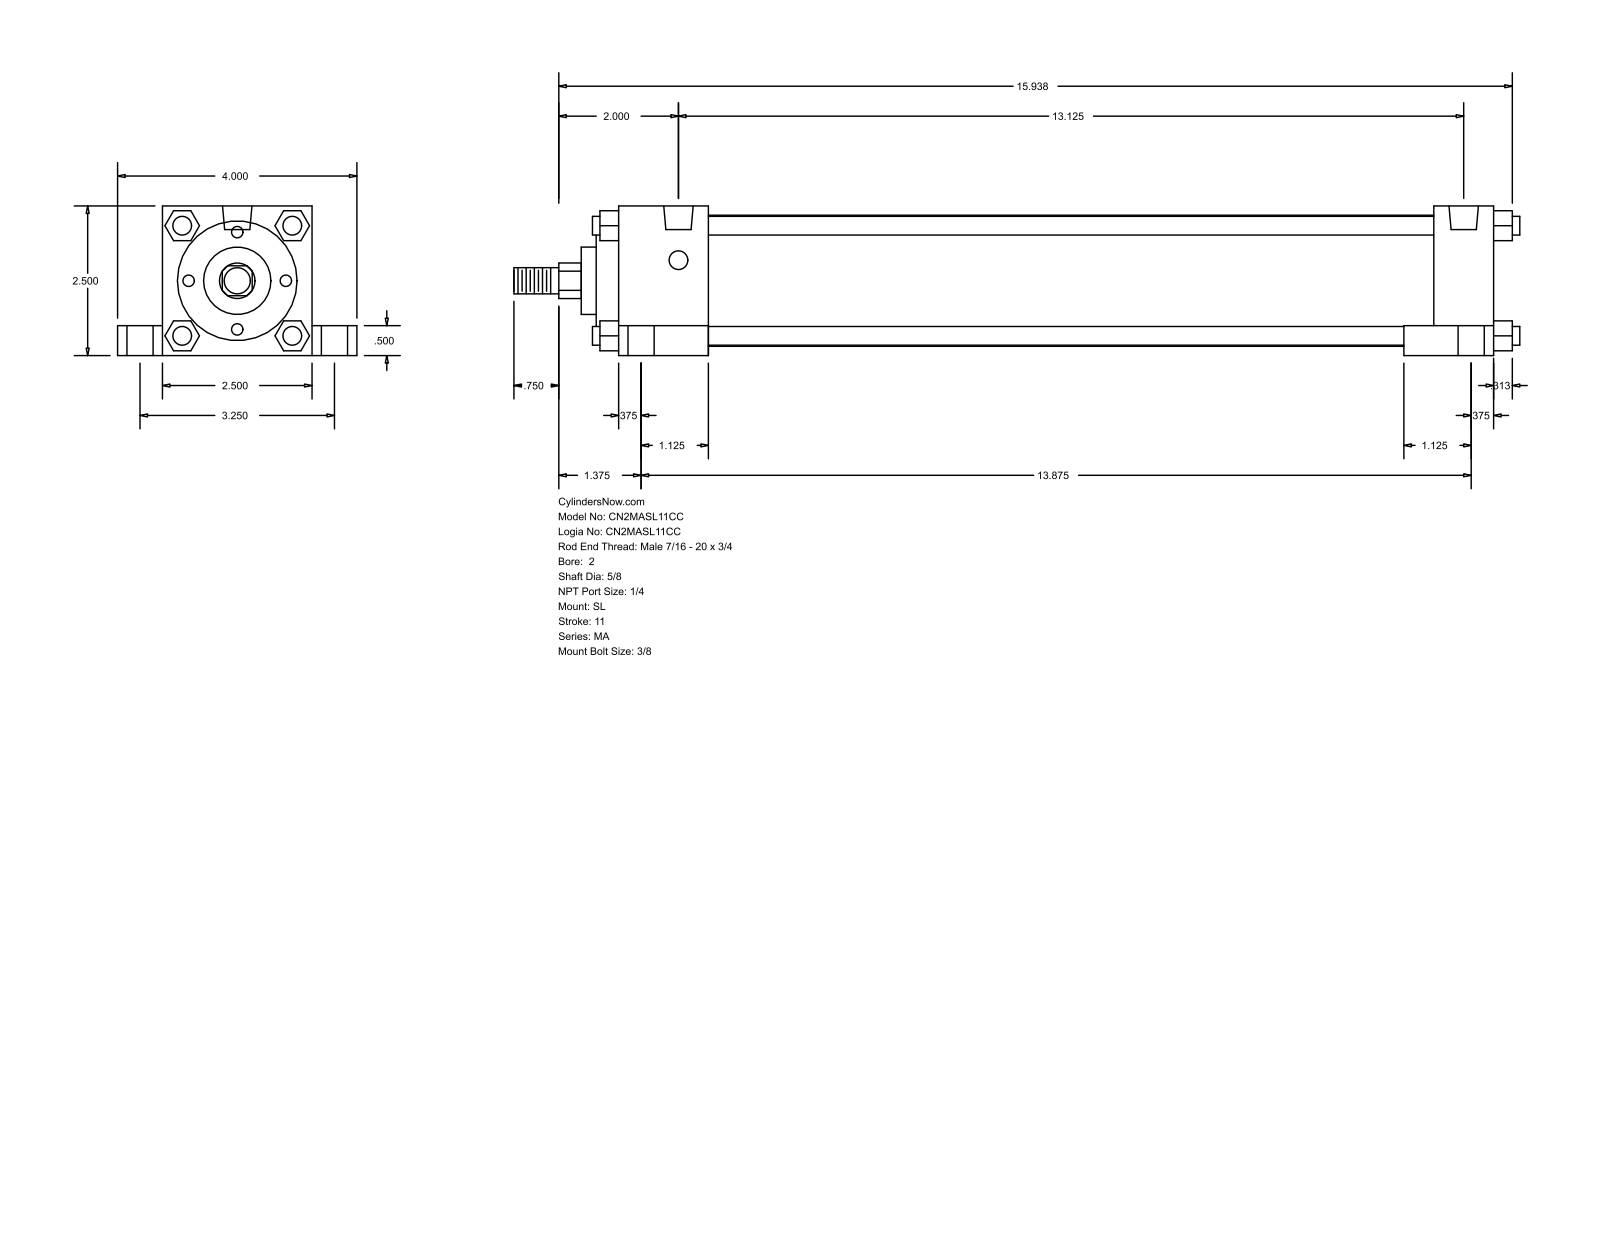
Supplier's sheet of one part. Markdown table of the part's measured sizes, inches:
| quantity | value |
| --- | --- |
| part name | MA_SL__0200_0.625 |
| STEP written by | GSSL Pune (CONFIG_CONTROL_DESIGN) |
| units | inches |
| bodies | 0 solids, 150 faces (113 planar, 37 cylindrical, 0 other) |
| overall size | 16.813 × 4 × 2.5 |
| round holes (diameter × count) | 0.313 × 4, 0.437 × 4, 0.687 × 4, 0.492 × 2 |
| round bosses / shafts (diameter × count) | 0.313 × 4, 2.19 × 1, 2 × 1, 1.125 × 1, 0.625 × 1, 0.437 × 1 |
| partial cylindrical surfaces (radius × count) | 0.297 × 1 |
| main face-to-face distances | 2.5, 0.5, 0.375, 1, 0.75, 3.25, 1.5, 14.625, 2, 13.125 |
| hole center spacings | 1.63, 1.741, 3.25, 13.125, 13.349, 13.846, 13.875, 14.251 |
